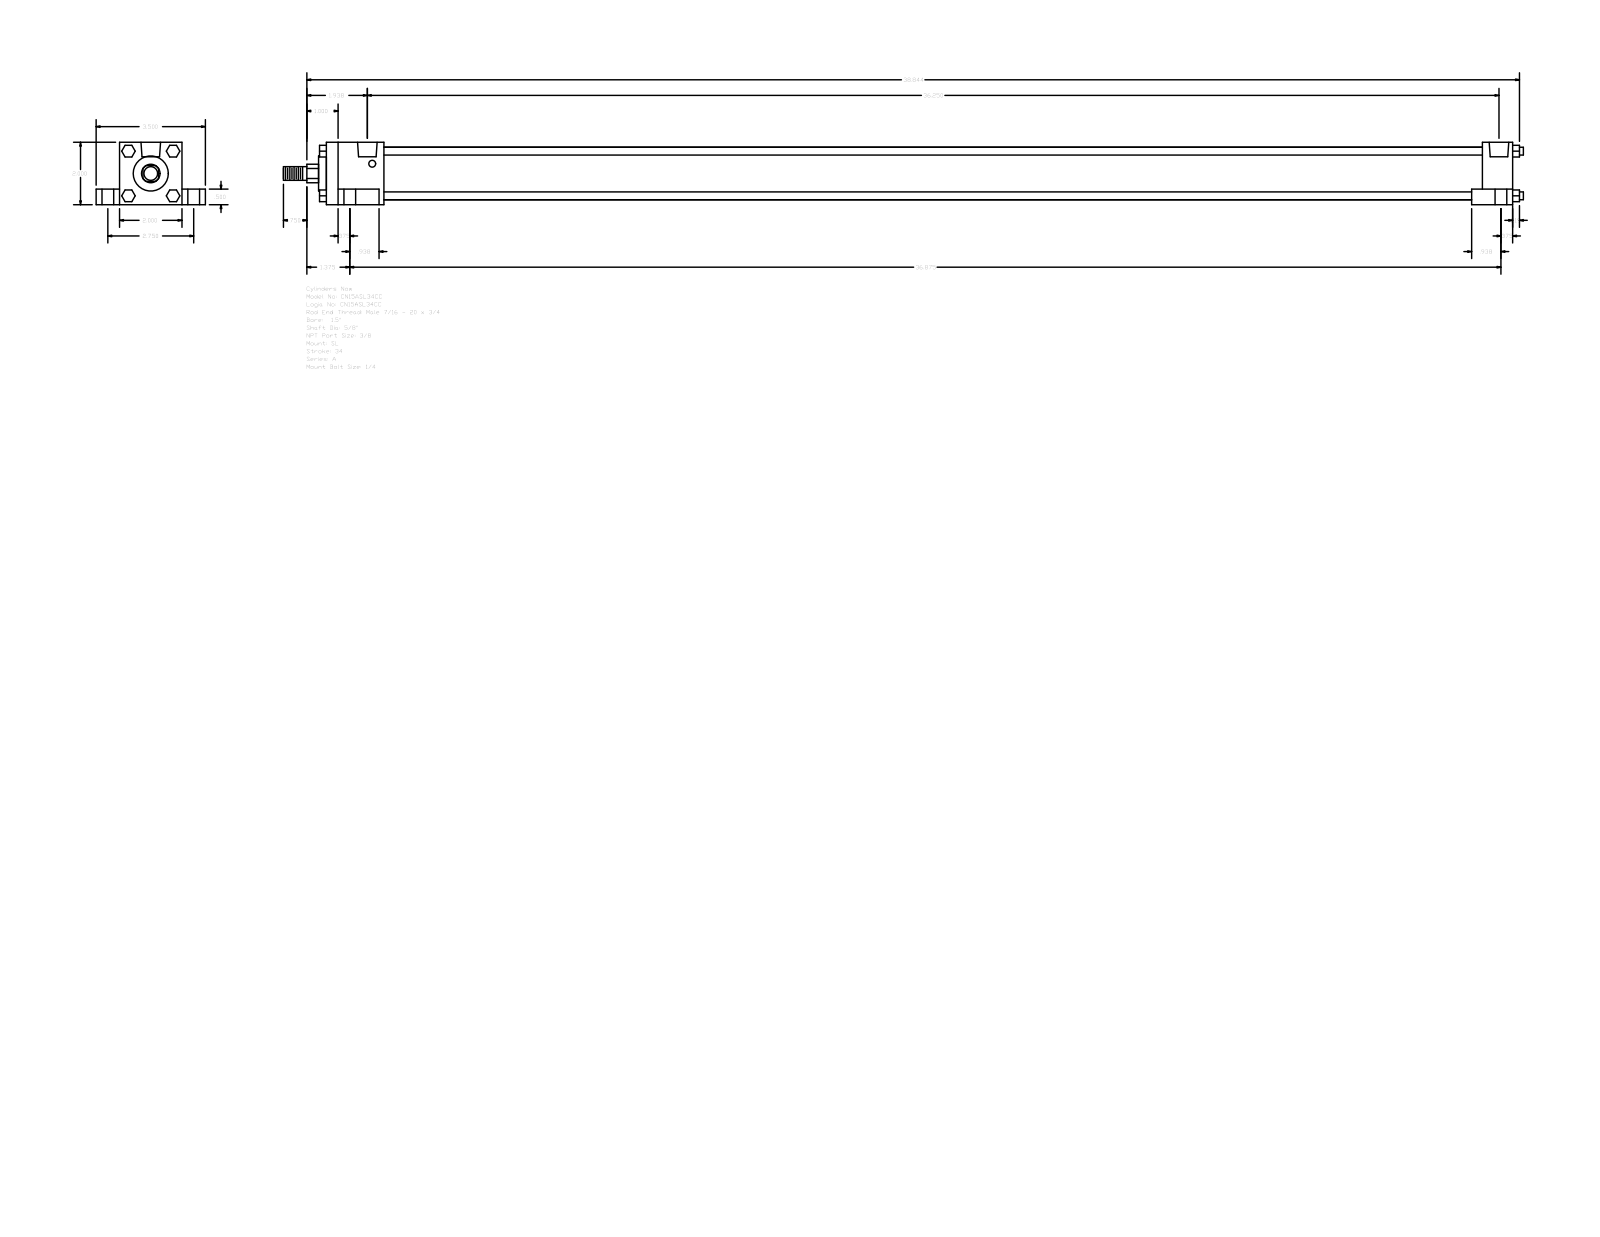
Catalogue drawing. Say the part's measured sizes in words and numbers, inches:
The part is named "A_SL__0150_0.625". Its 3-D file was written by "GSSL Pune (CONFIG_CONTROL_DESIGN)". It is 0 solids with 148 faces: 112 planar, 36 cylindrical and 0 other. Overall it measures 39.719 by 3.5 by 2 inches. Round holes: 4 of diameter 0.219, 4 of diameter 0.375, 4 of diameter 0.625, 2 of diameter 0.627. Round bosses or shafts: 4 of diameter 0.25, 1 of diameter 1.69, 1 of diameter 1.125, 1 of diameter 0.625, 1 of diameter 0.437. Partial cylindrical surfaces (rounded edges, fillets, slot ends): 1 of radius 0.297. The main face-to-face distances are 2, 0.75, 1.5, 0.5, 2.75, 38, 0.375, 1.313, 37.031, 0.969. The hole center spacings are 0.156, 1.376, 1.392, 1.485, 1.552, 2.75, 35.937, 36.094.
